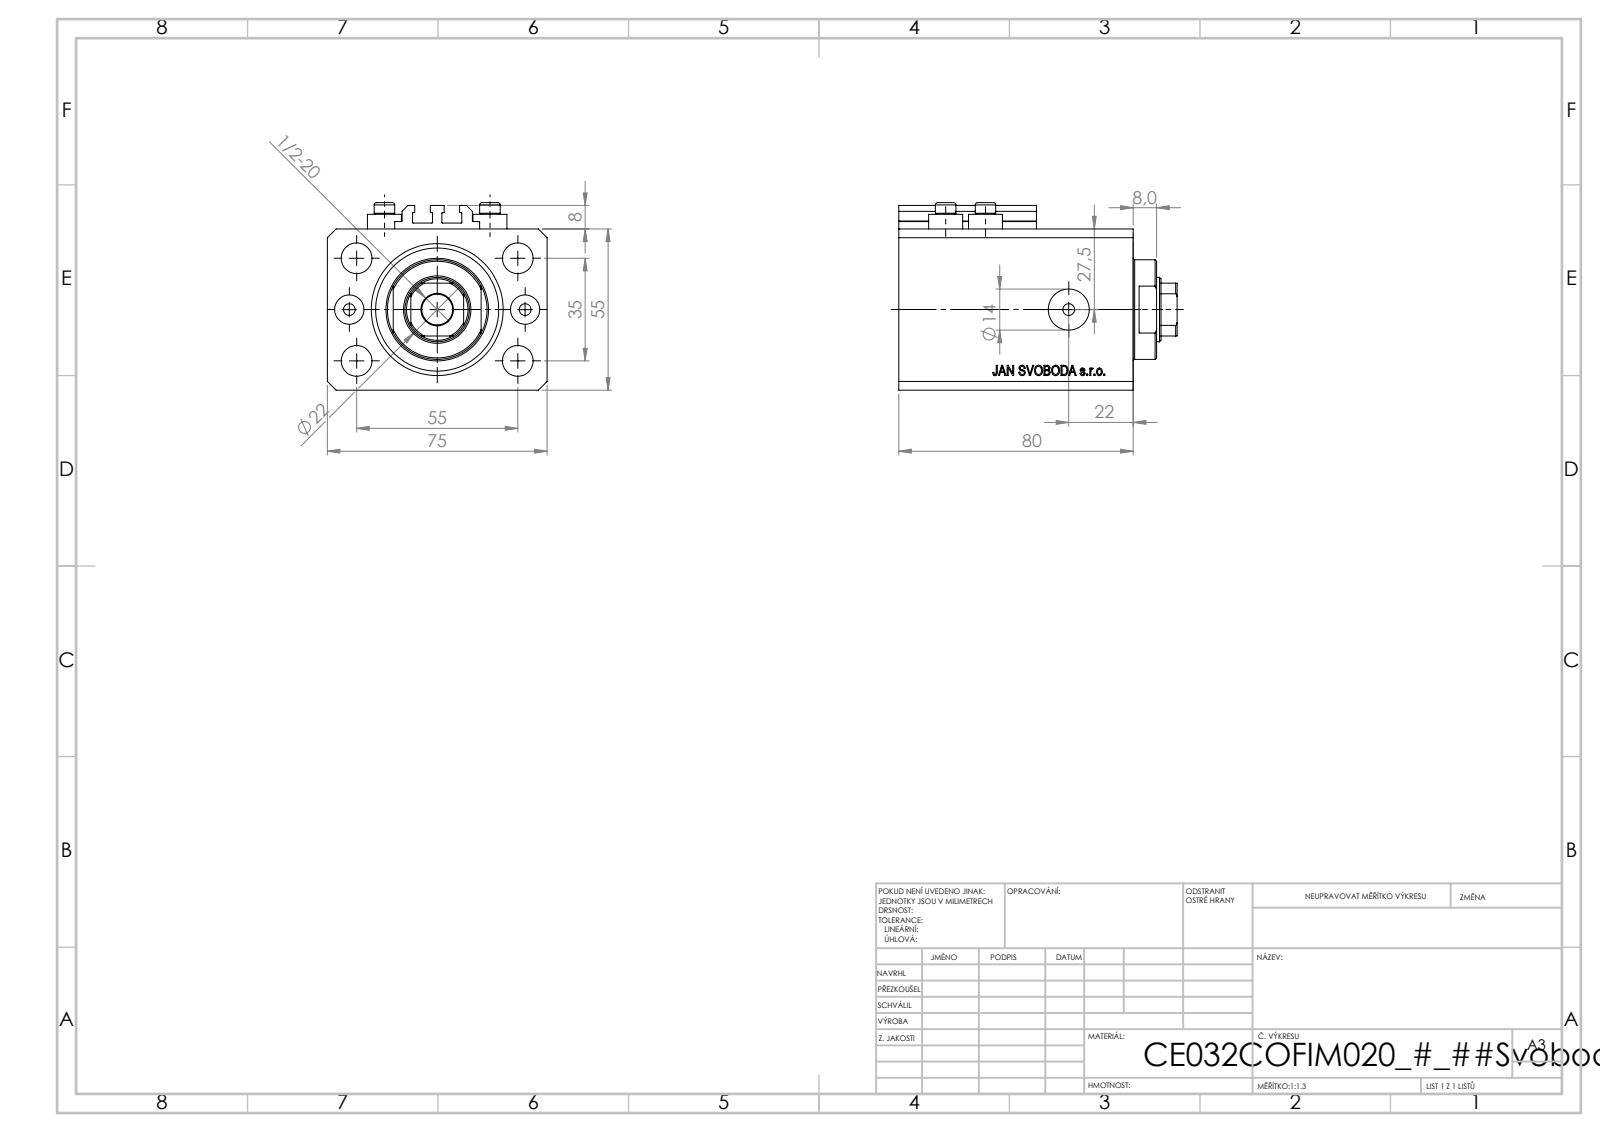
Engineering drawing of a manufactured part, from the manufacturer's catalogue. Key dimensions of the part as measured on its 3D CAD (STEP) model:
Part name (STEP PRODUCT): V250CE_VC_C; V250CE_C_VCP; V250CE_C_Body; ALLEN BOLT V250CE
STEP written by: SolidWorks 2019 (CONFIG_CONTROL_DESIGN)
Units: millimetres
Bodies: 8 solids, 1034 faces (504 planar, 86 cylindrical, 444 other)
Overall size (bounding box): 95 × 75 × 64
Volume: 305 050 mm³ · Surface area: 71 456 mm²
Round holes (diameter × count): ⌀4 ×8, ⌀10.5 ×5, ⌀10 ×2, ⌀14 ×2, ⌀22 ×1, ⌀32 ×1, ⌀45 ×1
Round bosses / shafts (diameter × count): ⌀11.6 ×4, ⌀7 ×4, ⌀34 ×1
Partial cylindrical surfaces — rounded edges, fillets, slot ends (radius × count): R0.2 ×10, R10.5 ×1
Main face-to-face distances: 55, 75, 80, 15, 65, 9.9, 55.1, 70.1, 3, 8
Hole centre spacings: 17.68, 32.6, 60.1, 36, 13.6, 30, 35, 38.48
